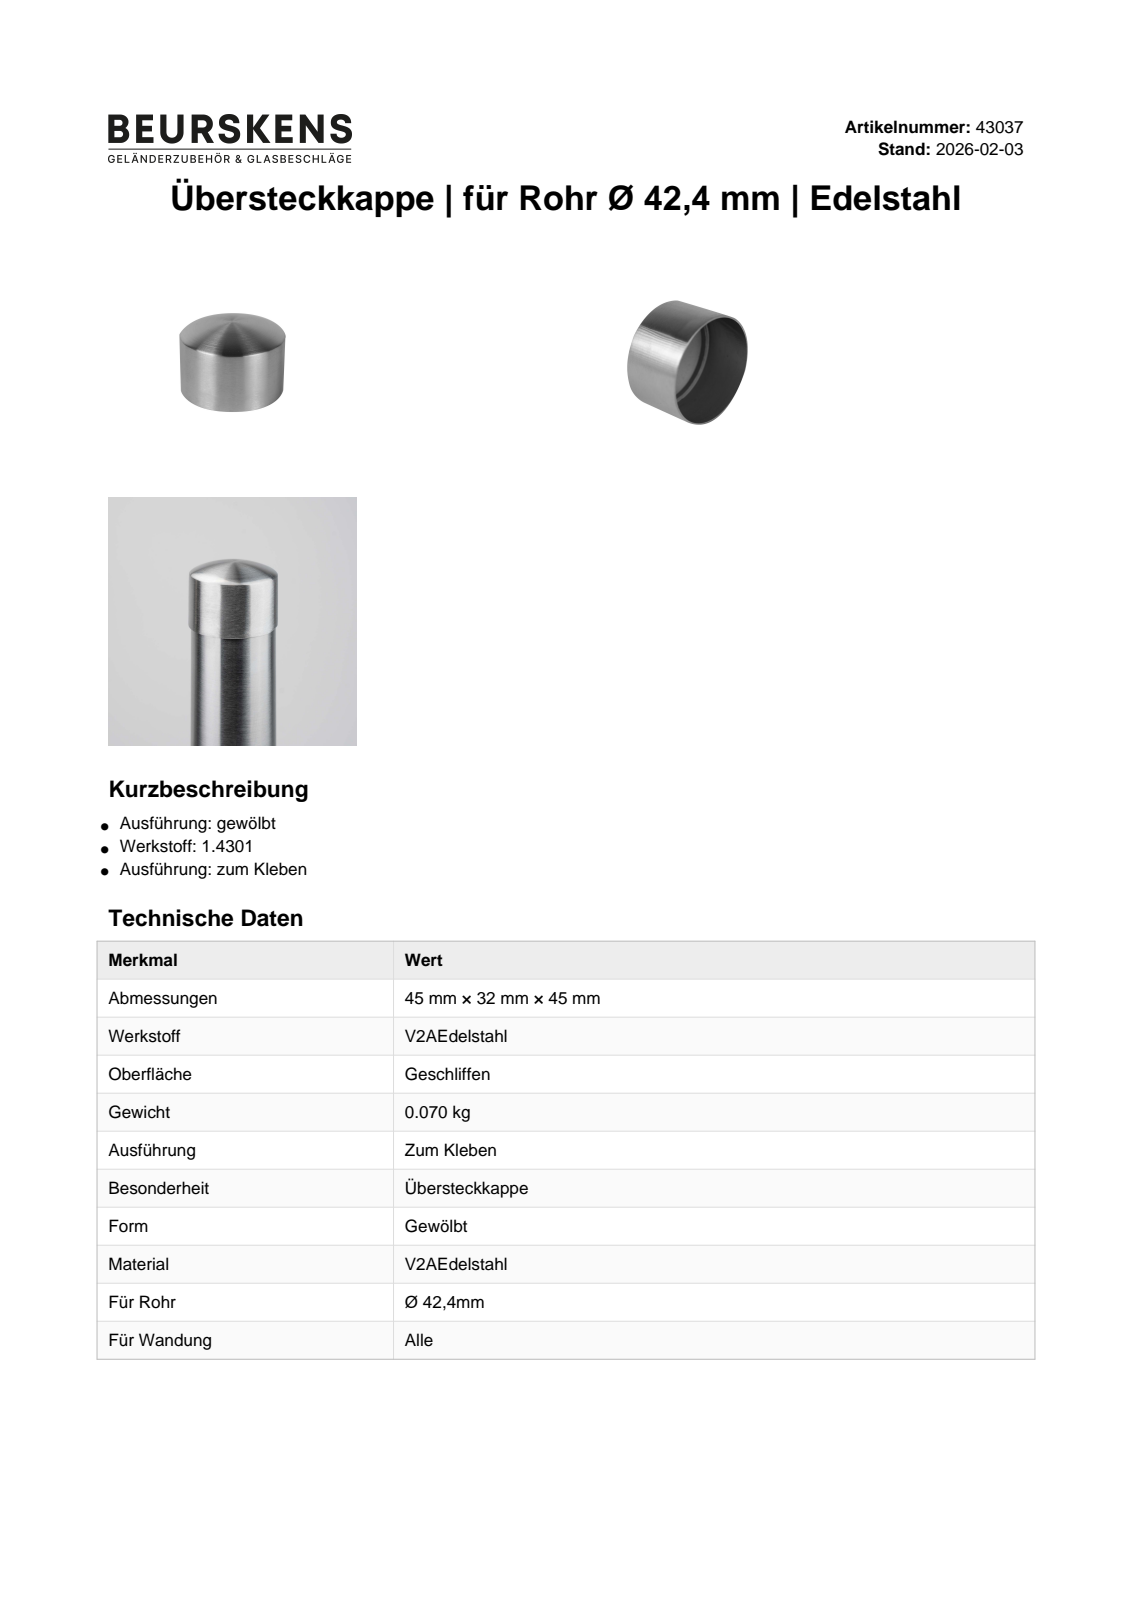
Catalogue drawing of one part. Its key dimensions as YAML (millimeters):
part_name: "43037"
step_written_by: "Autodesk Inventor 2022 (AUTOMOTIVE_DESIGN)"
units: millimeters
bodies: {solids: 1, faces: 8, planar: 2, cylindrical: 3, other: 3}
overall_size: [44.4, 44.4, 30.2]
volume: 5219
surface_area: 10025
round_holes:
  - {diameter: 40, count: 1}
  - {diameter: 42.7, count: 1}
round_bosses_or_shafts:
  - {diameter: 44.4, count: 1}
face_to_face_distances: [20]
